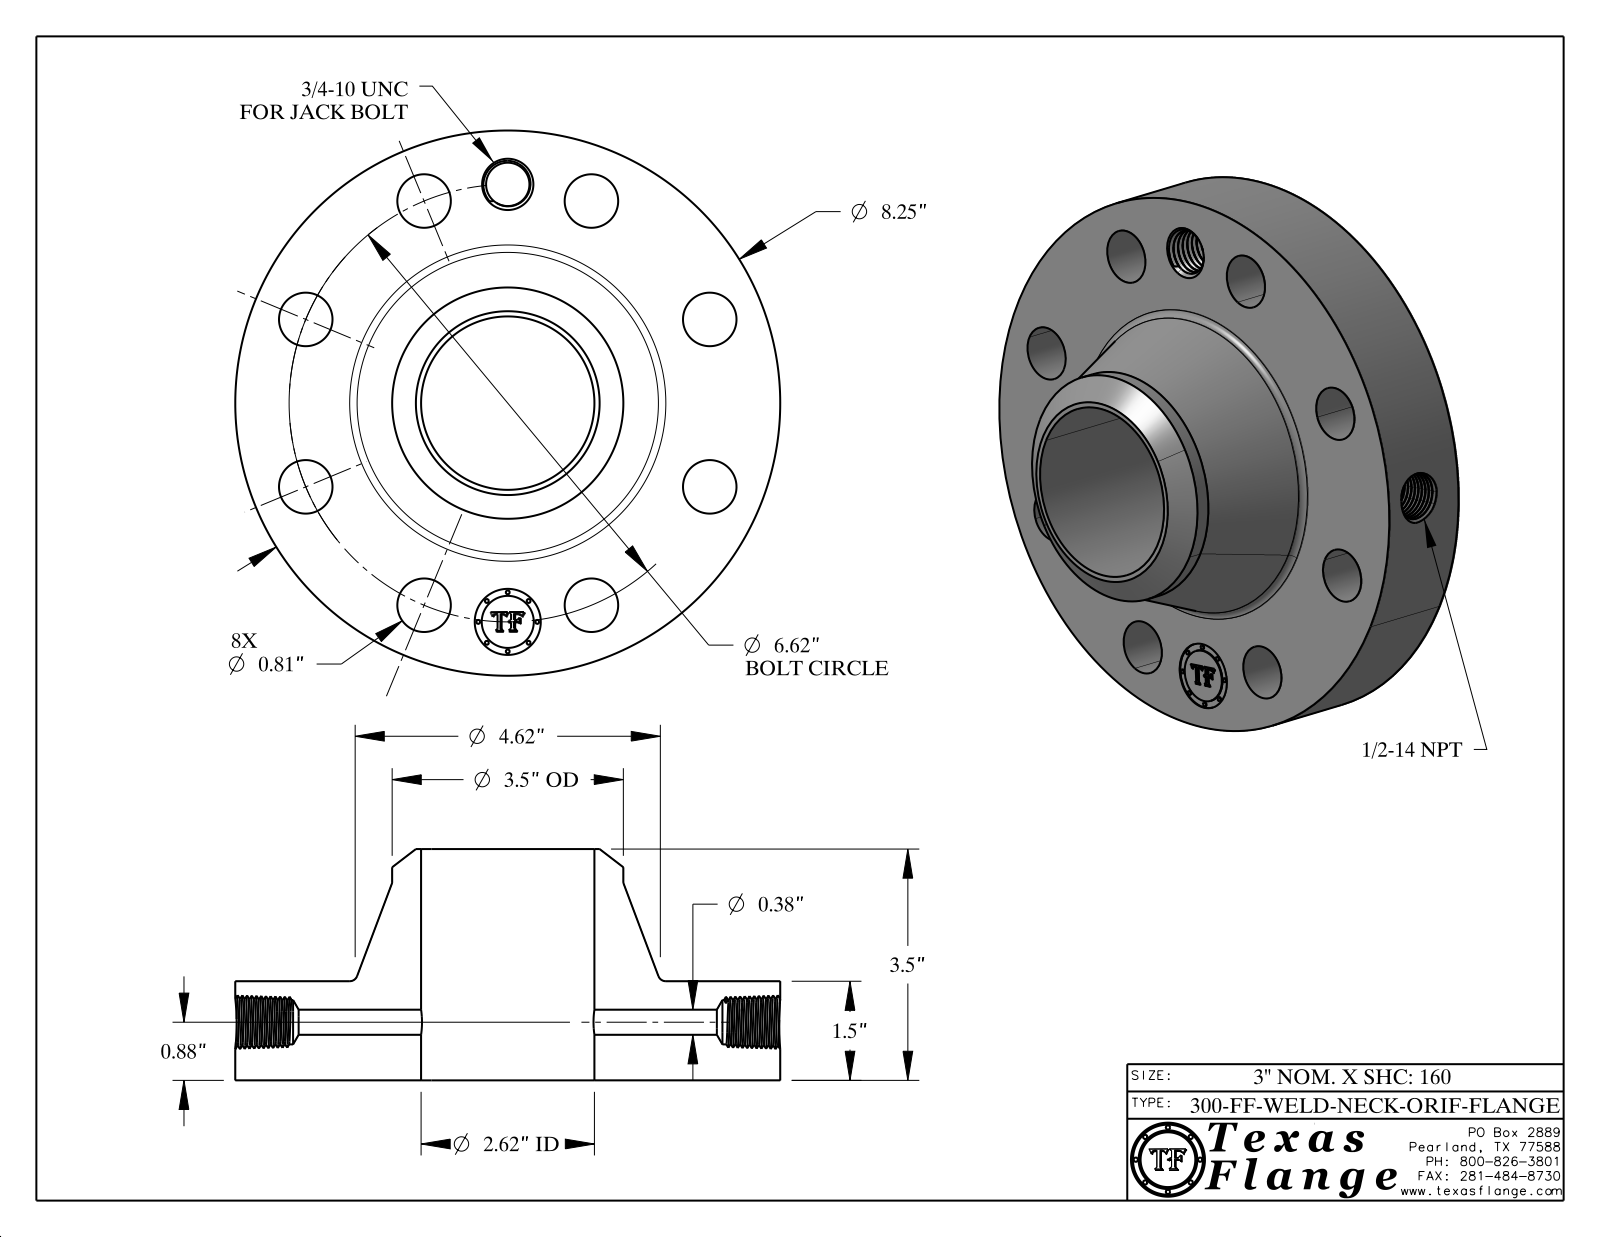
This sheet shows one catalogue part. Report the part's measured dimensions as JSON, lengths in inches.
{"part_name": "300-FF-WELD-NECK", "step_written_by": "CATIA V5 STEP AP214 (AUTOMOTIVE_DESIGN)", "units": "inches", "bodies": {"solids": 1, "faces": 766, "planar": 368, "cylindrical": 90, "other": 308}, "overall_size": [8.25, 8.25, 3.5], "volume_in3": 77.11, "surface_area_in2": 217.4, "round_holes": [[0.81, 8], [0.38, 1], [0.656, 1], [0.672, 1], [1, 1], [2.624, 1]], "round_bosses_or_shafts": [[0.061, 8], [8.25, 1], [3.5, 1], [0.788, 1]], "face_to_face_distances": [1.5, 3.5, 2, 0.015, 1.485, 2.015, 0.298, 0.293, 0.054, 0.248], "hole_center_spacings": [3.31, 4.681, 6.116, 6.62, 1.291, 2.533, 2.533, 3.678]}
